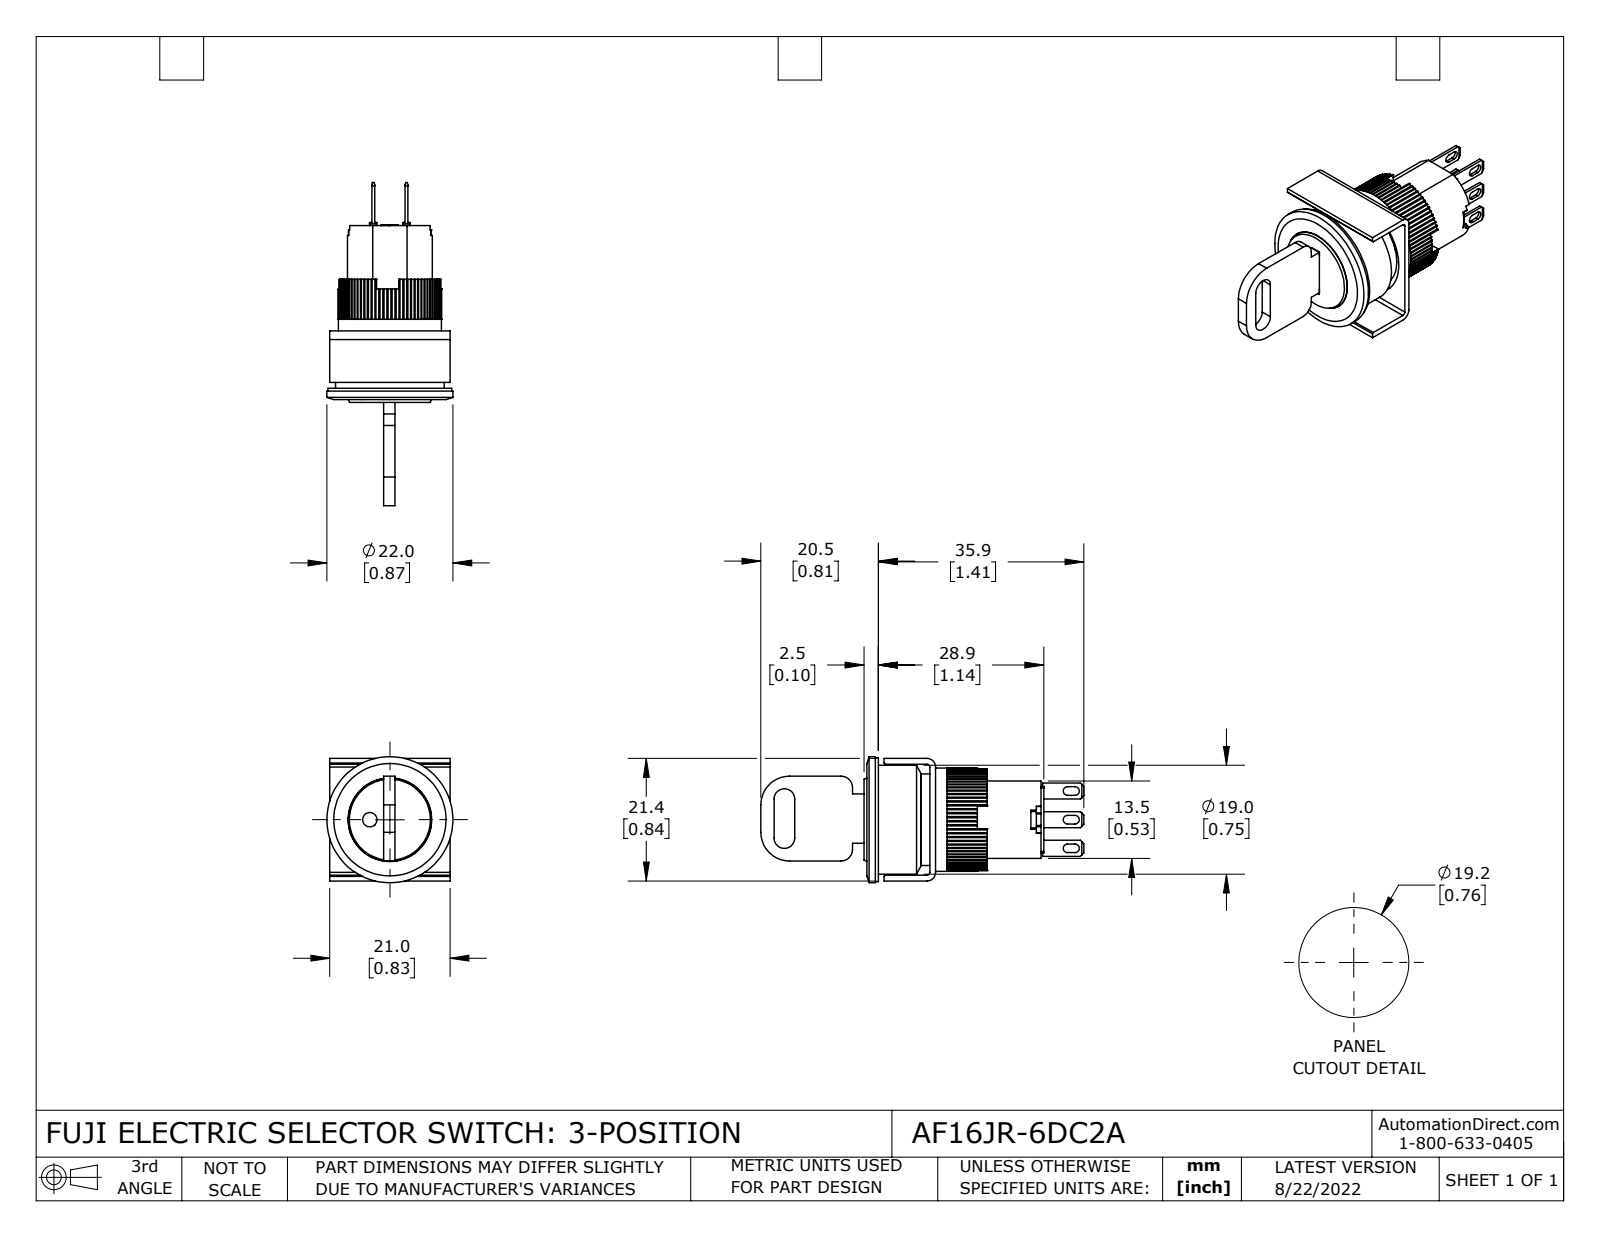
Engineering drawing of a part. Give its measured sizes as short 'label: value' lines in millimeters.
name: AF16JR-6DC2A
written by: SolidWorks 2021 (CONFIG_CONTROL_DESIGN)
unit: mm
bodies: 13 solids, 707 faces (518 planar, 183 cylindrical, 6 other)
size: 56.4 × 22 × 22
volume: 8 110 mm³; area: 7 252 mm²
holes: 1× ⌀1, 1× ⌀2.5, 1× ⌀14.6, 1× ⌀18, 1× ⌀19
bosses: 1× ⌀22, 1× ⌀21.6, 1× ⌀16, 1× ⌀14.8, 1× ⌀14.5
rounds: 80× R0.3, 12× R0.2, 6× R0.8, 2× R0.5, 2× R1.5, 2× R1.8, 2× R2, 2× R5
face distances: 2, 1, 0.5, 9.5, 4.5, 2.5, 10, 20.4, 1.5, 19.4
hole spacings: 3.5
